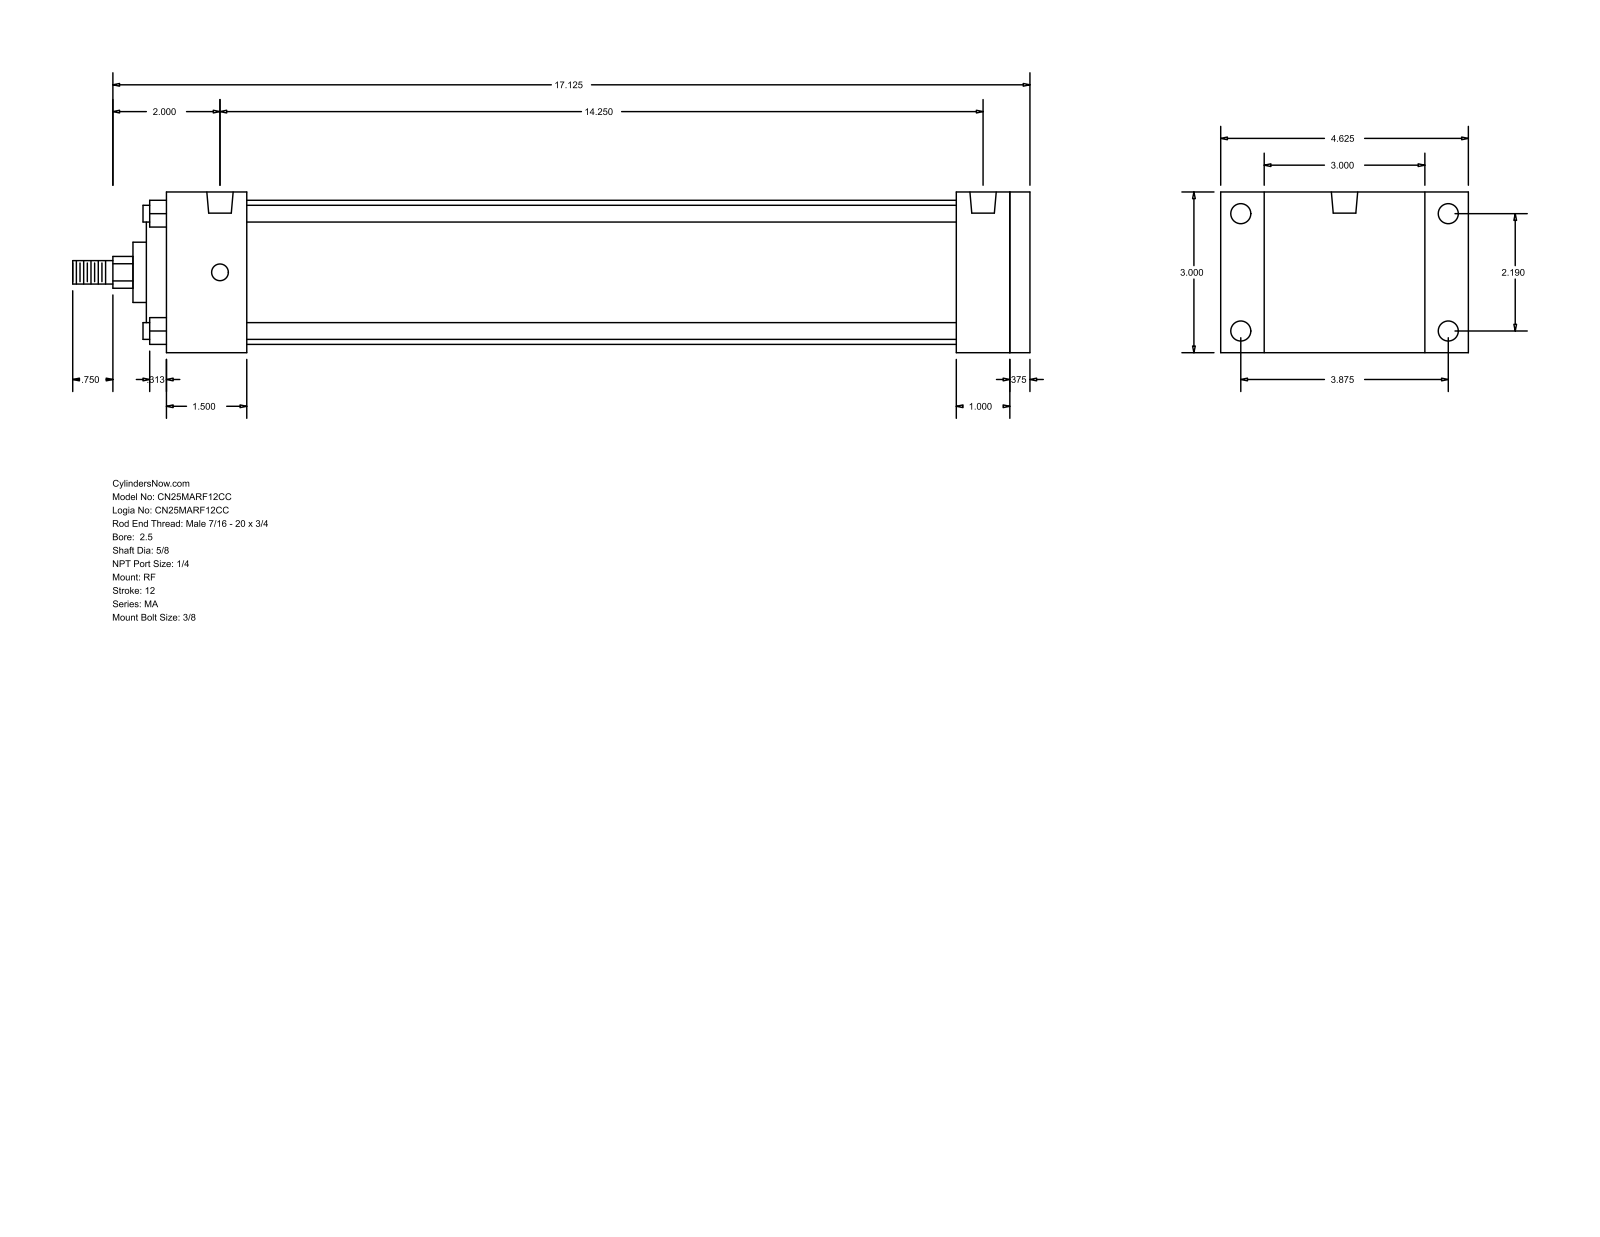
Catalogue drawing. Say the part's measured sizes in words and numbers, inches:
The part is named "MA_RF__0250_0.625". Its 3-D file was written by "GSSL Pune (CONFIG_CONTROL_DESIGN)". It is 0 solids with 94 faces: 65 planar, 29 cylindrical and 0 other. Overall it measures 17.875 by 4.625 by 3 inches. Round holes: 4 of diameter 0.313, 4 of diameter 0.375, 2 of diameter 0.492. Round bosses or shafts: 4 of diameter 0.313, 1 of diameter 2.69, 1 of diameter 2, 1 of diameter 1.125, 1 of diameter 0.625, 1 of diameter 0.437. Partial cylindrical surfaces (rounded edges, fillets, slot ends): 1 of radius 0.297. The main face-to-face distances are 3, 16.125, 0.375, 15.75, 1, 1.375, 1.5, 14.75, 13.25, 14.25. The hole center spacings are 2.19, 3.875, 4.451, 14.25.
